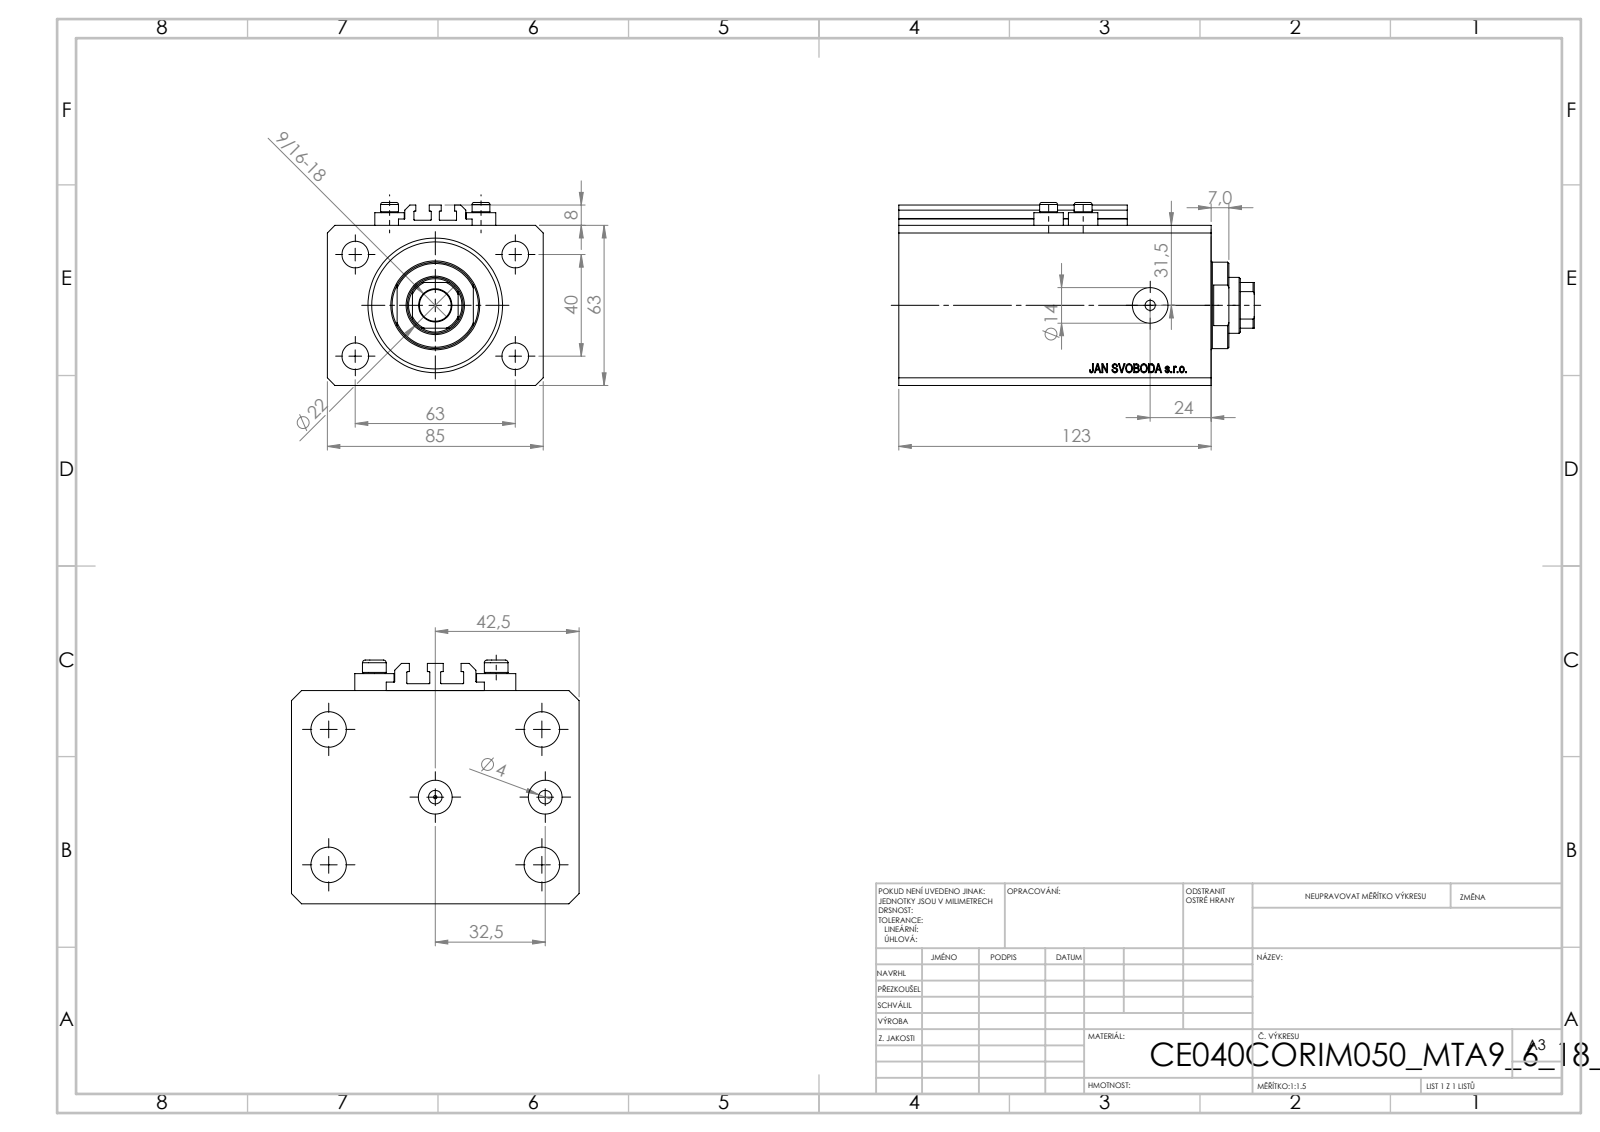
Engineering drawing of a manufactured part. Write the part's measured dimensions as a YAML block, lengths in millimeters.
part_name: "V250CE_C_Body; ALLEN BOLT V250CE; V250CE_VC_C; V250CE_C_VCP"
step_written_by: "SolidWorks 2019 (CONFIG_CONTROL_DESIGN)"
units: millimeters
bodies: {solids: 8, faces: 1038, planar: 504, cylindrical: 88, other: 446}
overall_size: [140, 85, 72]
volume: 586857
surface_area: 114184
round_holes:
  - {diameter: 4, count: 8}
  - {diameter: 10.5, count: 4}
  - {diameter: 10, count: 2}
  - {diameter: 14, count: 2}
  - {diameter: 1.25, count: 1}
  - {diameter: 12.5, count: 1}
  - {diameter: 22, count: 1}
  - {diameter: 40, count: 1}
  - {diameter: 53, count: 1}
round_bosses_or_shafts:
  - {diameter: 11.6, count: 4}
  - {diameter: 7, count: 4}
  - {diameter: 34, count: 1}
partial_cylinders:
  - {radius: 0.2, count: 10}
  - {radius: 10.5, count: 1}
face_to_face_distances: [63, 85, 123, 17, 106, 11.4, 94.6, 111.6, 2.5, 10]
hole_center_spacings: [37.31, 13.6, 20.02, 36, 38.48, 40, 63, 67.05]
